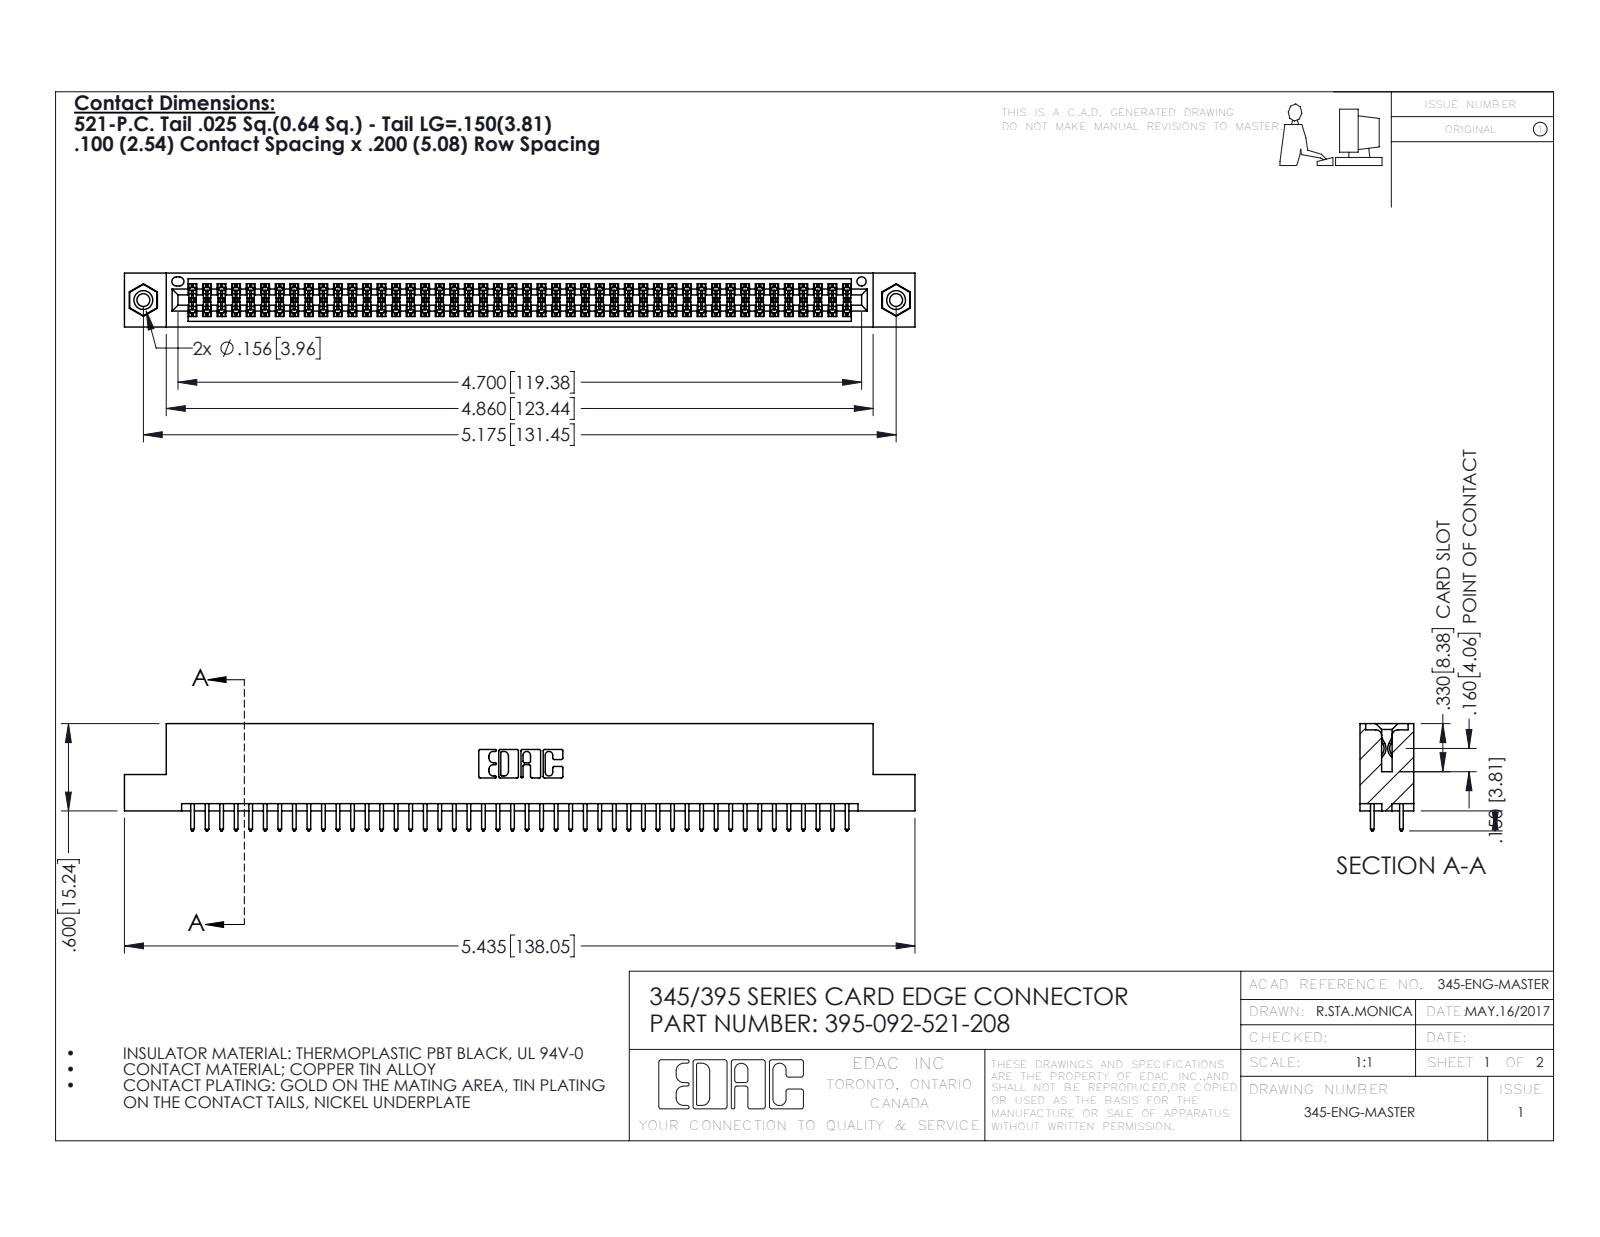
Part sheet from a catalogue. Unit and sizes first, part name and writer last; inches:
Units: inches
Overall size (bounding box): 5.435 × 0.737 × 0.37
Round holes (diameter × count): ⌀0.089 ×2, ⌀0.125 ×2, ⌀0.156 ×2, ⌀0.064 ×1
Round bosses / shafts (diameter × count): ⌀0.155 ×2
Partial cylindrical surfaces — rounded edges, fillets, slot ends (radius × count): R0.006 ×138, R0.01 ×92, R0.01 ×22, R0.007 ×6, R0.031 ×6, R0.026 ×3, R0.014 ×2, R0.019 ×2
Main face-to-face distances: 0.072, 0.298, 0.2, 0.37, 0.098, 0.272, 0.025, 0.225, 0.175, 0.149
Hole centre spacings: 0.27, 4.939, 5.175
Volume: 0.818 in³ · Surface area: 30.47 in²
Bodies: 95 solids, 4786 faces (3148 planar, 1622 cylindrical, 16 other)
Part name (STEP PRODUCT): 345-292-001_345-293-121; 345-250-001_345-250-003-102; 395-092-521-208; 345 Part_Flush Mounting Lugs - 0.156 Dia-TI
STEP written by: SolidWorks 2016 (CONFIG_CONTROL_DESIGN)
